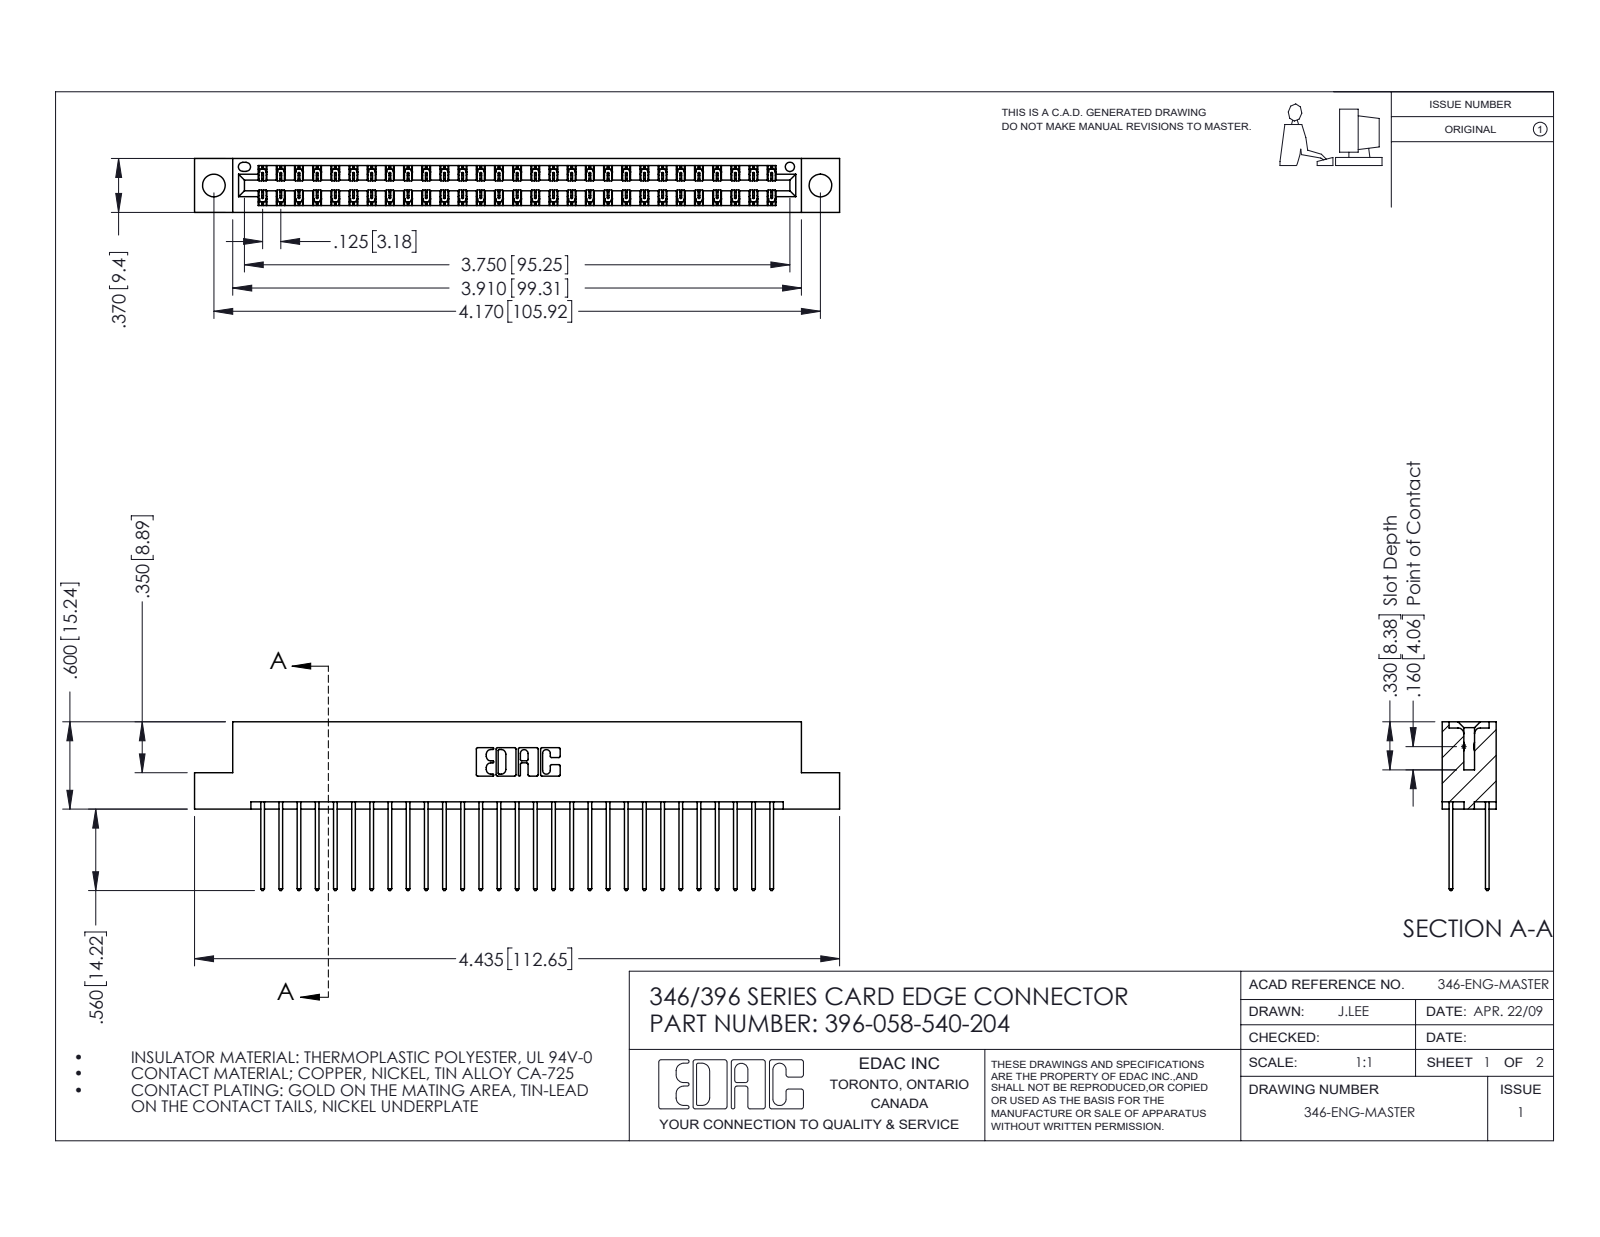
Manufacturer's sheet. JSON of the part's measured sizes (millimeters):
{"part_name": "345-292-001_345-293-140; 346 Part_Flush Mounting Lugs - 0.156 Dia-TH; 396-058-540-204", "step_written_by": "SolidWorks 2016 (CONFIG_CONTROL_DESIGN)", "units": "millimeters", "bodies": {"solids": 59, "faces": 3138, "planar": 2106, "cylindrical": 1032, "other": 0}, "overall_size": [112.6, 29.5, 9.4], "volume_mm3": 11000, "surface_area_mm2": 15790, "round_holes": [[4, 2], [1.6, 1]], "partial_cylinders_radius": [[0.2, 87], [0.3, 58], [0.3, 22], [0.2, 6], [0.8, 6], [0.7, 3], [0.4, 2], [0.6, 2]], "face_to_face_distances": [1.2, 8.2, 6.4, 1.8, 7.6, 0.6, 9.4, 7, 3.8, 5.6], "hole_center_spacings": [6.2, 100.6, 105.9]}
